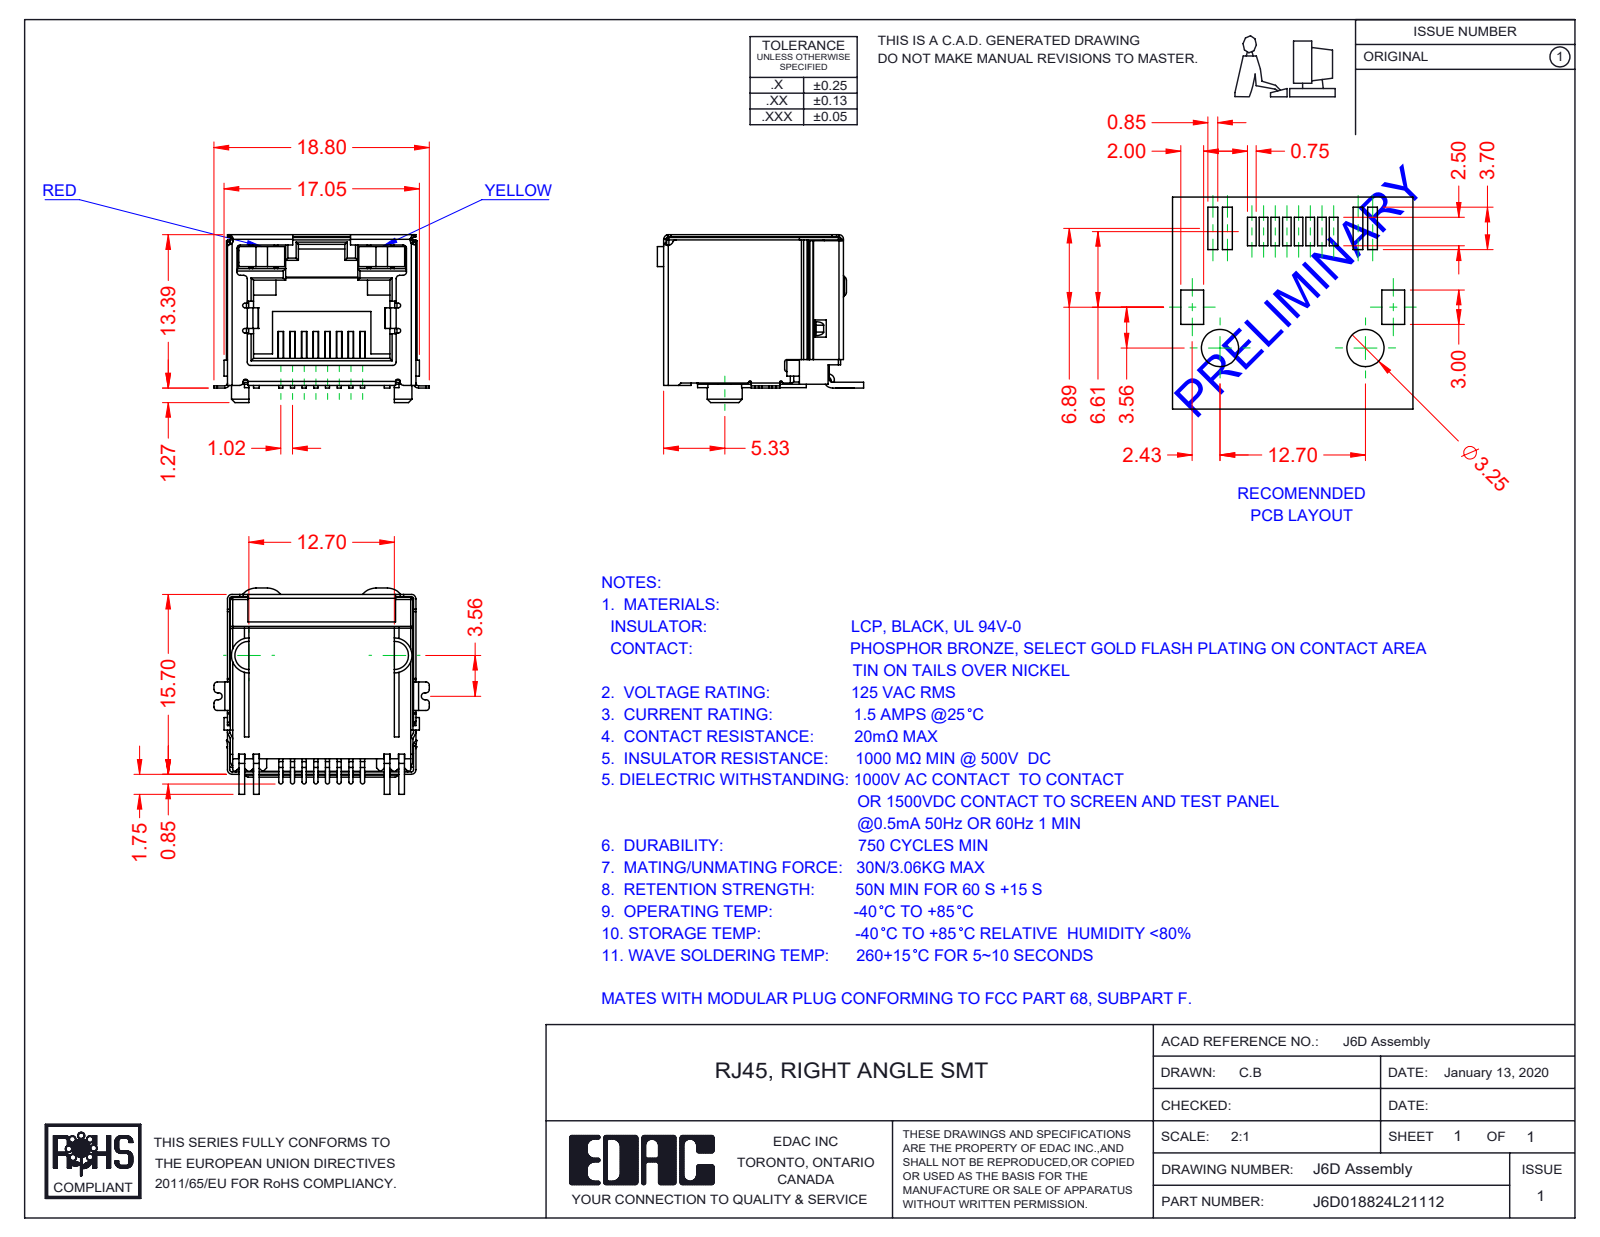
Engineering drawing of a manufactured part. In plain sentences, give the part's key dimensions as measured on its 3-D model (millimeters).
The part is named "6D Shield_LED - No EMI; J6D018824L21112; 6D LED RH_1-Yellow; 6D LED LH_2-Red (+2 more)". Its 3-D file was written by "SolidWorks 2016 (CONFIG_CONTROL_DESIGN)". It is 12 solids with 893 faces: 644 planar, 216 cylindrical and 33 other. Overall it measures 18.8 by 18 by 14.65 millimeters. Its volume is 1 804 cubic millimeters and its surface area 4 898 square millimeters. Partial cylindrical surfaces (rounded edges, fillets, slot ends): 39 of radius 0.3, 37 of radius 0.2, 16 of radius 0.4, 12 of radius 0.1, 8 of radius 0.15, 8 of radius 0.18, 6 of radius 0.5, 5 of radius 1.5. The main face-to-face distances are 16, 16.25, 16.2, 2.25, 1, 15.95, 16.05, 12.8, 0.45, 16.45.
